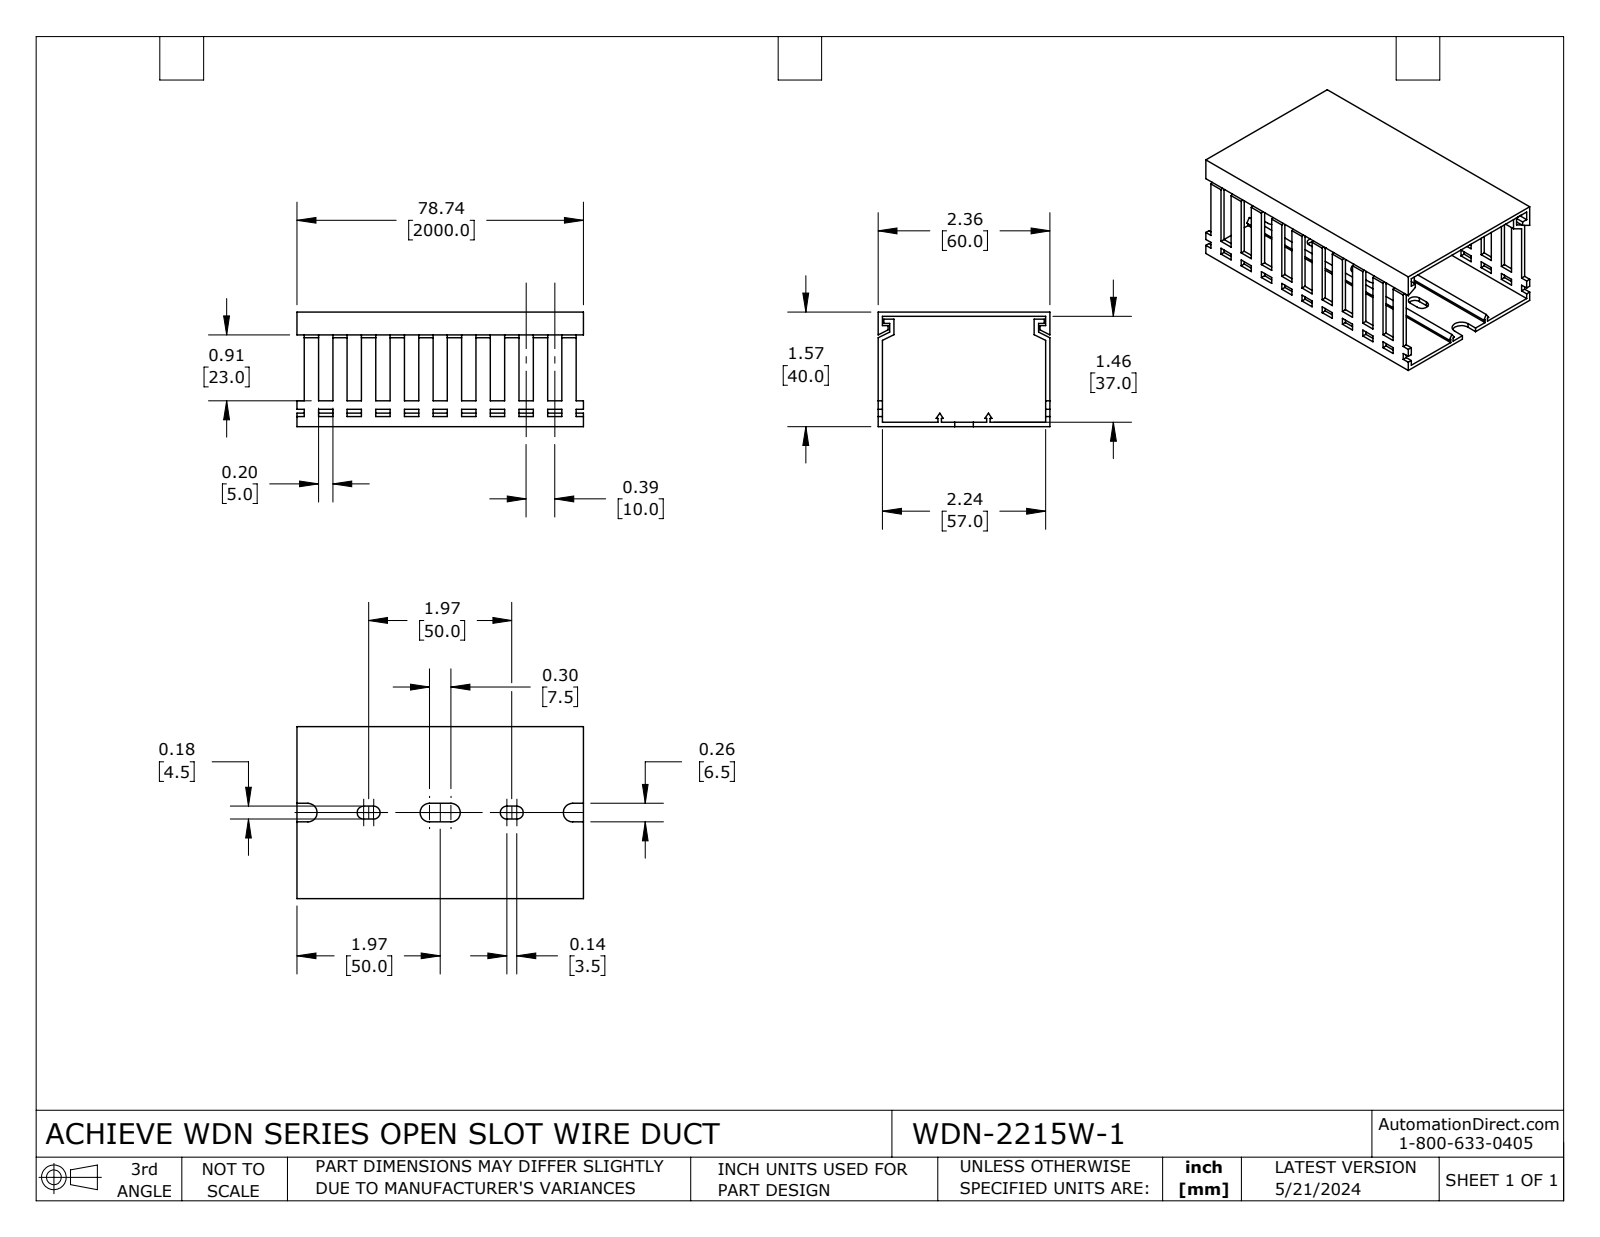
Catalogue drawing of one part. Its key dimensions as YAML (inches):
part_name: "WDN-2215W-1"
step_written_by: "SolidWorks 2023 (CONFIG_CONTROL_DESIGN)"
units: inches
bodies: {solids: 2, faces: 350, planar: 338, cylindrical: 12, other: 0}
overall_size: [3.937, 2.362, 1.575]
volume: 1.702
surface_area: 63.3
partial_cylinders:
  - {radius: 0.089, count: 4}
  - {radius: 0.128, count: 4}
face_to_face_distances: [0.059, 1.516, 1.575, 1.457, 2.303, 2.362, 2.244, 0.394, 0.197, 0.591]
